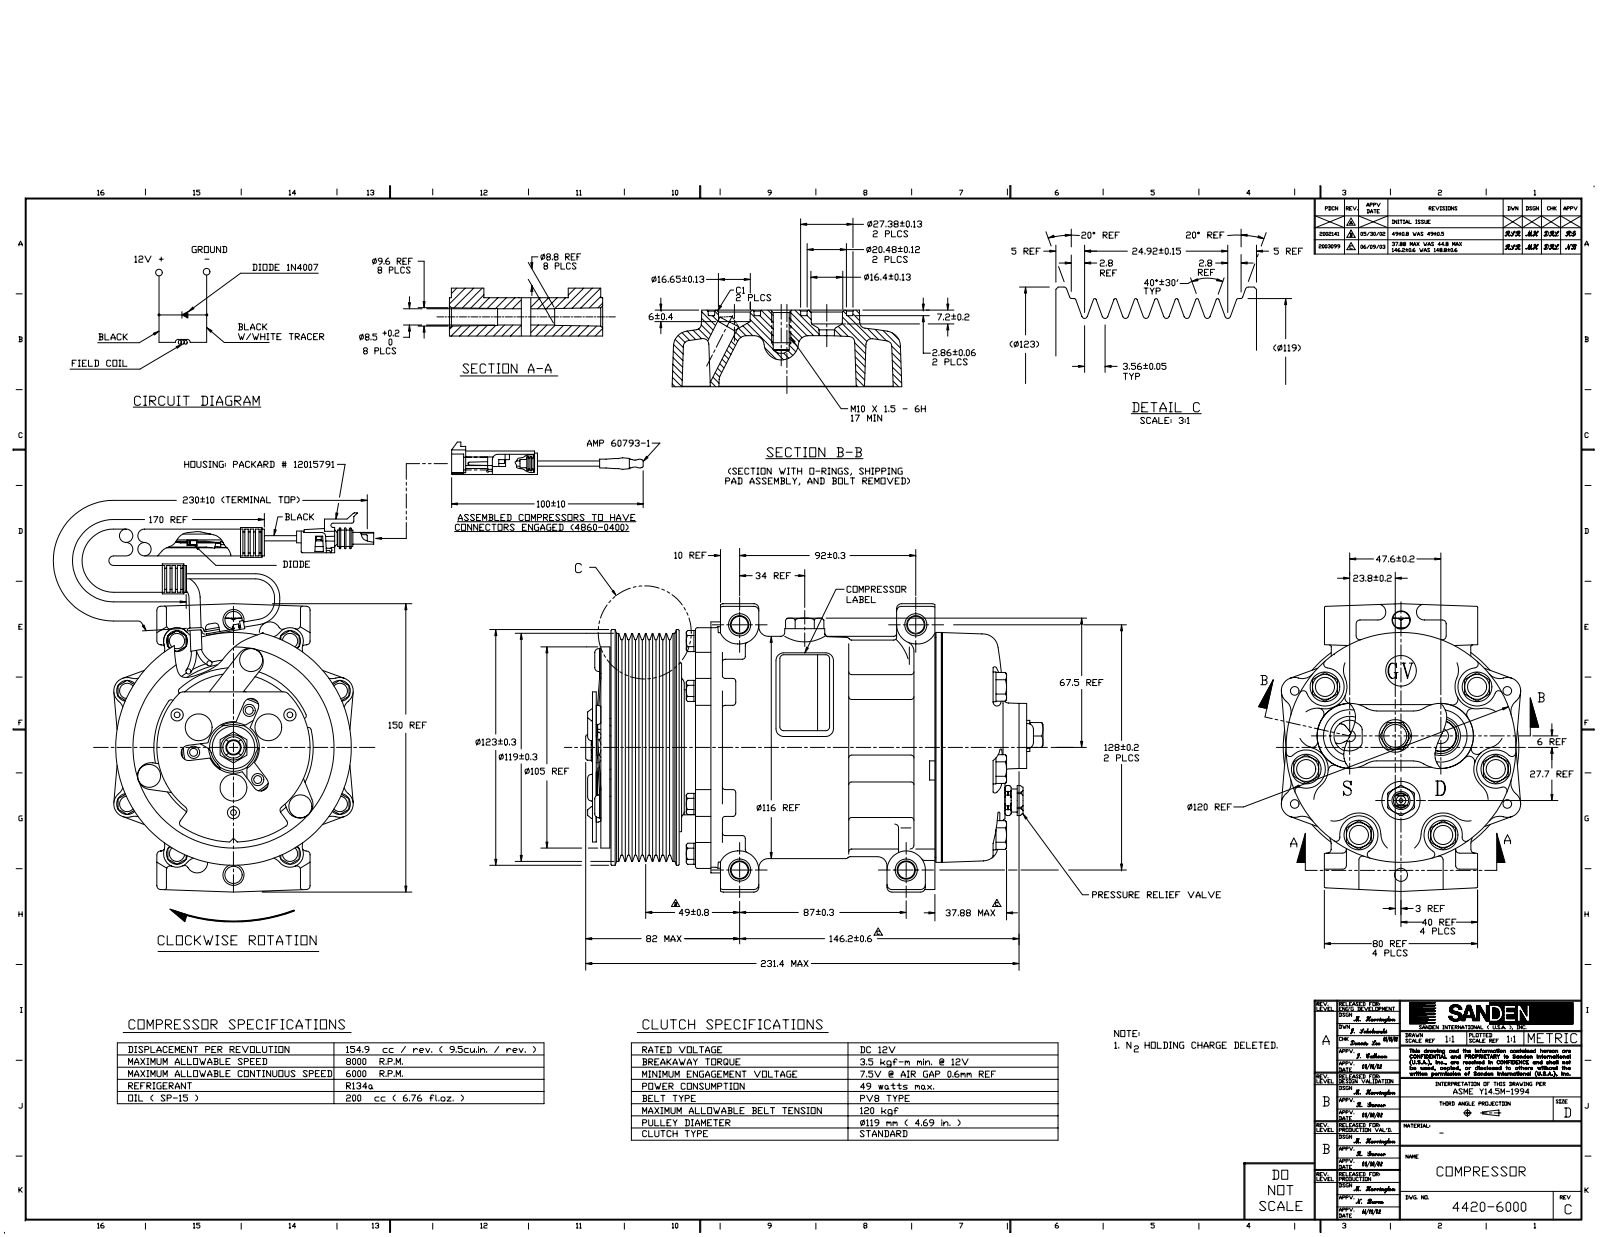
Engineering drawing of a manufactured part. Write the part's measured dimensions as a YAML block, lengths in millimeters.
part_name: "SANDEN_4420_REV_C_COMPR_AC"
step_written_by: "SolidWorks 2007 (CONFIG_CONTROL_DESIGN)"
units: millimeters
bodies: {solids: 1, faces: 2698, planar: 696, cylindrical: 673, other: 1329}
overall_size: [453.83, 231.04, 125]
volume: 2279000
surface_area: 266636
round_holes:
  - {diameter: 8.5, count: 13}
  - {diameter: 11.9, count: 6}
  - {diameter: 8, count: 4}
  - {diameter: 2.2, count: 3}
  - {diameter: 5.08, count: 3}
  - {diameter: 6.6, count: 3}
  - {diameter: 9, count: 2}
  - {diameter: 27.38, count: 2}
  - {diameter: 3.5, count: 1}
  - {diameter: 6.7, count: 1}
  - {diameter: 10, count: 1}
  - {diameter: 11, count: 1}
round_bosses_or_shafts:
  - {diameter: 12.9, count: 8}
  - {diameter: 15.3, count: 6}
  - {diameter: 2.7, count: 6}
  - {diameter: 12, count: 4}
  - {diameter: 5.69, count: 4}
  - {diameter: 14, count: 3}
  - {diameter: 10, count: 3}
  - {diameter: 7.9, count: 3}
partial_cylinders:
  - {radius: 7, count: 41}
  - {radius: 2, count: 35}
  - {radius: 0.5, count: 32}
  - {radius: 3, count: 30}
  - {radius: 2.5, count: 20}
  - {radius: 1.5, count: 18}
  - {radius: 5, count: 17}
  - {radius: 10, count: 15}
face_to_face_distances: [2, 46.54, 44.94, 4.4, 8.6, 5.6, 50.54, 8.4, 6.4, 38.54]
hole_center_spacings: [62.85, 88.89, 31.48, 36.77, 46.4, 59, 66.7, 110.89]
